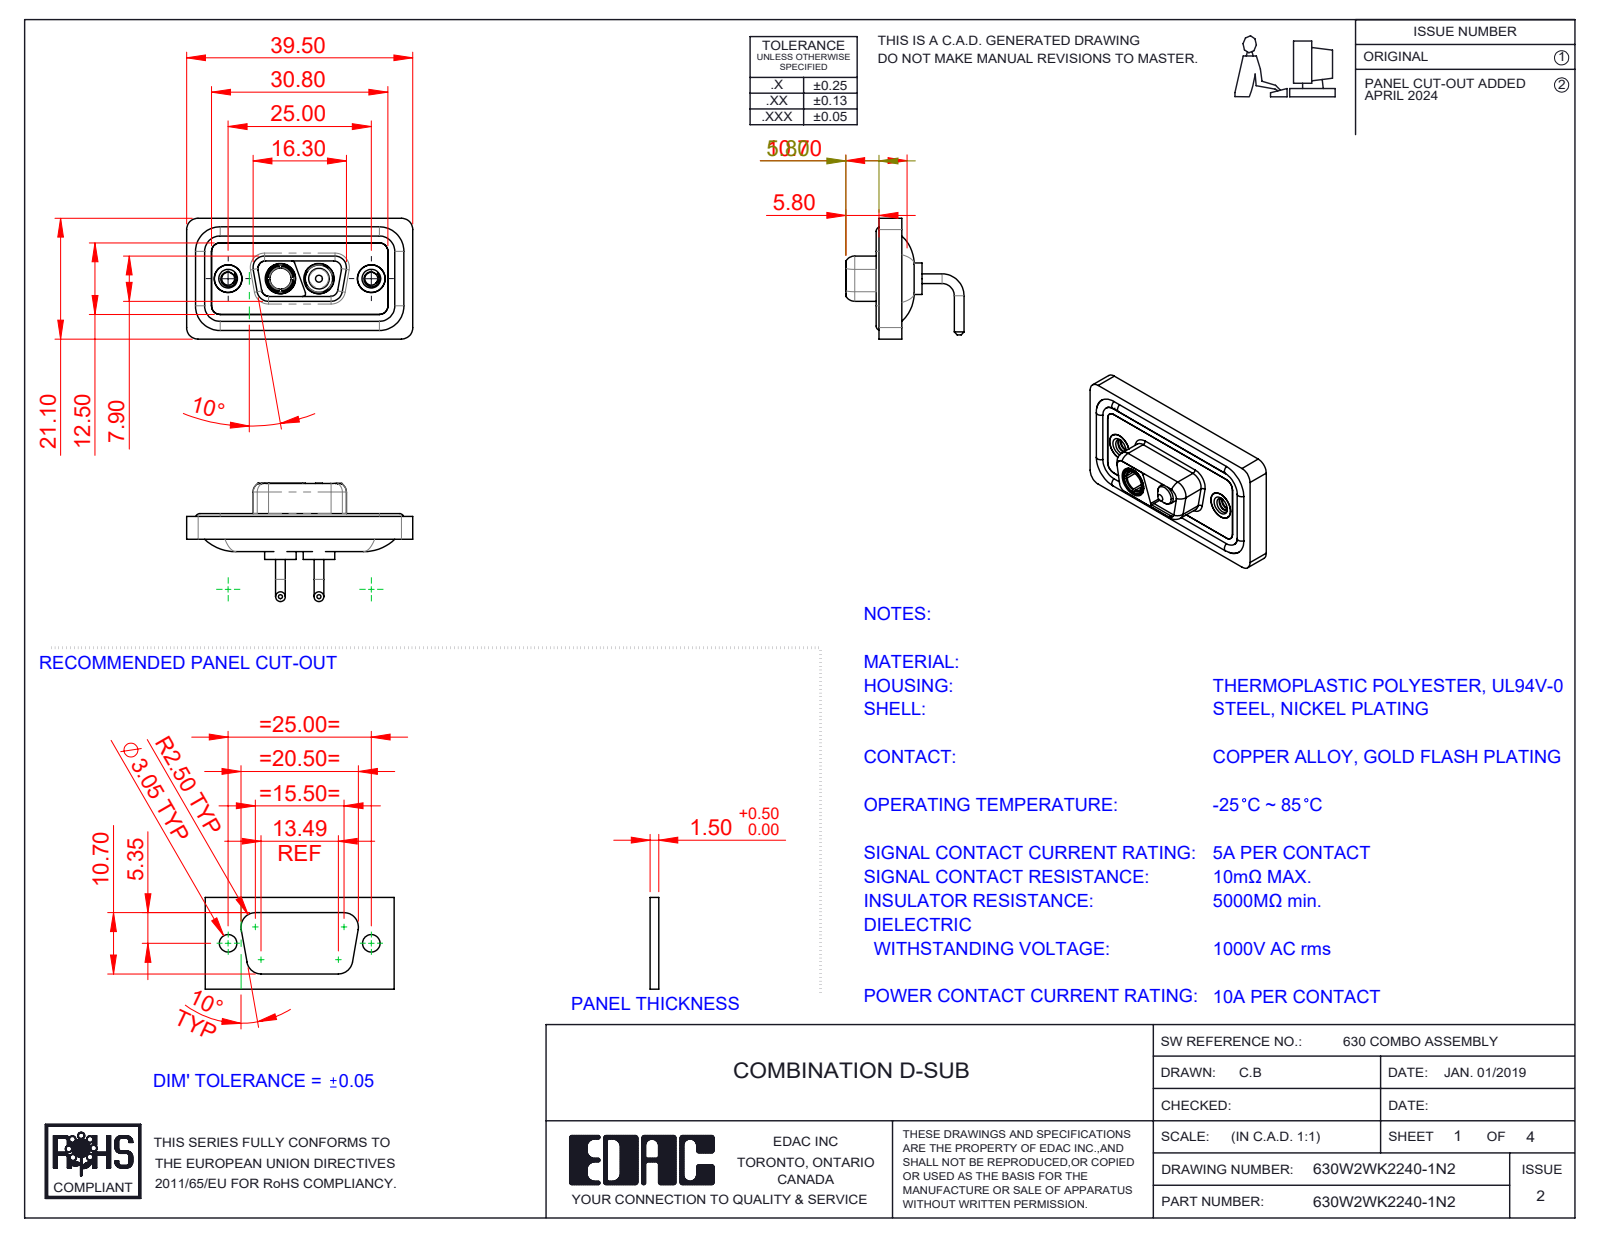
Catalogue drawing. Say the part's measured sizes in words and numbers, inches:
The part is named "630Combo Housing_2WK2; 630Combo Waterproof Housing_09 Contacts; 630Combo Shell Rear_09 Contacts; 630Combo Threaded Rivet_2 (+4 more)". Its 3-D file was written by "SolidWorks 2023 (CONFIG_CONTROL_DESIGN)". It is 11 solids with 508 faces: 144 planar, 235 cylindrical and 129 other. Overall it measures 1.555 by 0.831 by 0.813 inches. Its volume is 0.28 cubic inches and its surface area 11.46 square inches. Round holes: 4 of diameter 0.191, 2 of diameter 0.089, 2 of diameter 0.157, 2 of diameter 0.159, 2 of diameter 0.197, 2 of diameter 0.209, 1 of diameter 0.146. Round bosses or shafts: 4 of diameter 0.067, 4 of diameter 0.063, 2 of diameter 0.217, 2 of diameter 0.205, 2 of diameter 0.195, 2 of diameter 0.189, 2 of diameter 0.187, 2 of diameter 0.148. Partial cylindrical surfaces (rounded edges, fillets, slot ends): 18 of radius 0.059, 18 of radius 0.079, 8 of radius 0.053, 8 of radius 0.063, 6 of radius 0.02, 4 of radius 0.01, 4 of radius 0.024, 4 of radius 0.026. The main face-to-face distances are 0.016, 0.043, 0.114, 0.071, 0.098, 0.063, 0.122, 0.059, 0.083, 0.146. The hole center spacings are 0.36, 0.624, 0.265, 0.984.
